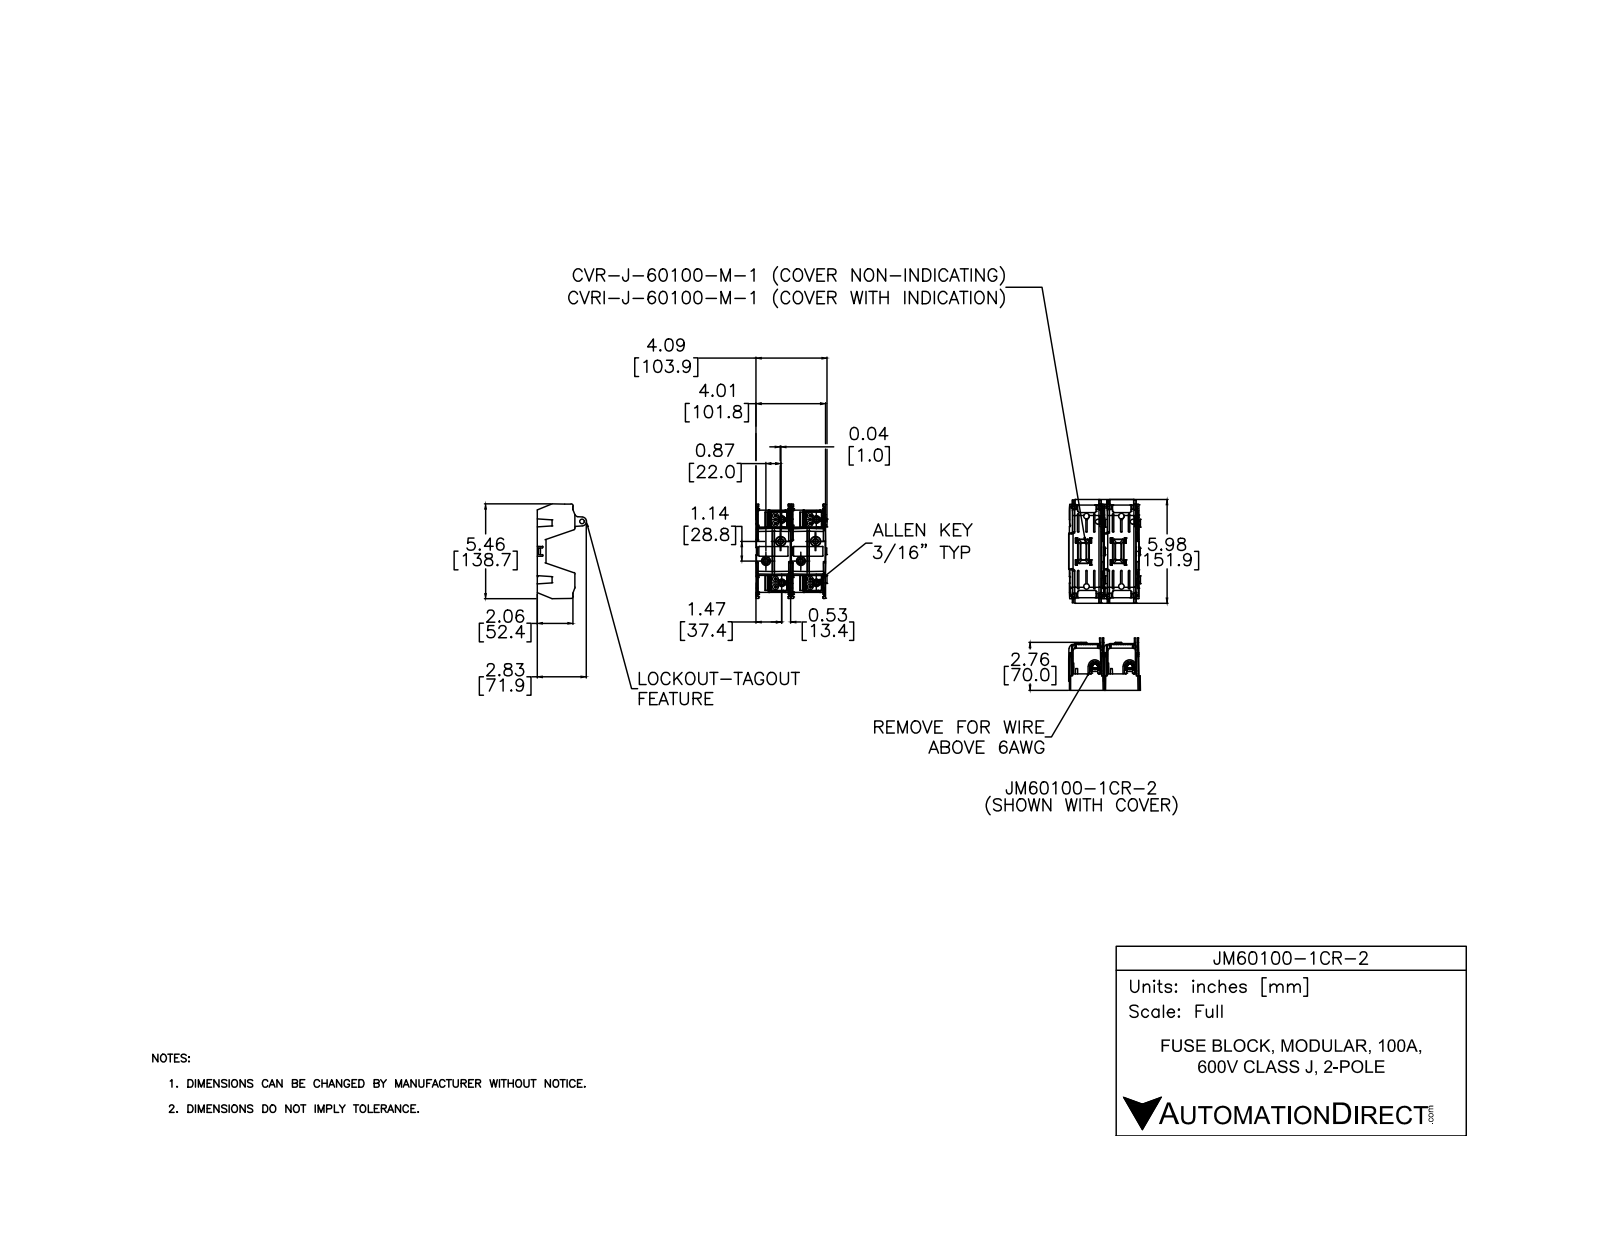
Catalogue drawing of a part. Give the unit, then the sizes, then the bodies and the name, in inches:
Units: inches
Overall size (bounding box): 5.463 × 4.103 × 2.829
Round holes (diameter × count): ⌀0.19 ×4, ⌀0.25 ×4
Round bosses / shafts (diameter × count): ⌀0.306 ×8, ⌀0.039 ×8, ⌀0.437 ×4, ⌀0.437 ×4, ⌀0.406 ×2, ⌀0.236 ×2, ⌀0.277 ×1
Partial cylindrical surfaces — rounded edges, fillets, slot ends (radius × count): R0.02 ×142, R0.01 ×88, R0.015 ×66, R0.02 ×48, R0.01 ×46, R0.03 ×16, R0.079 ×14, R0.158 ×10
Main face-to-face distances: 2.01, 1.898, 3.908, 0.112, 0.95, 0.025, 0.247, 3.674, 0.025, 0.974
Hole centre spacings: 3.674, 0.07, 0.535, 3.675, 3.713
Bodies: 0 solids, 1762 faces (562 planar, 770 cylindrical, 430 other)
Part name (STEP PRODUCT): JM60100-1CR-2
STEP written by: SolidWorks 2021 (CONFIG_CONTROL_DESIGN)
